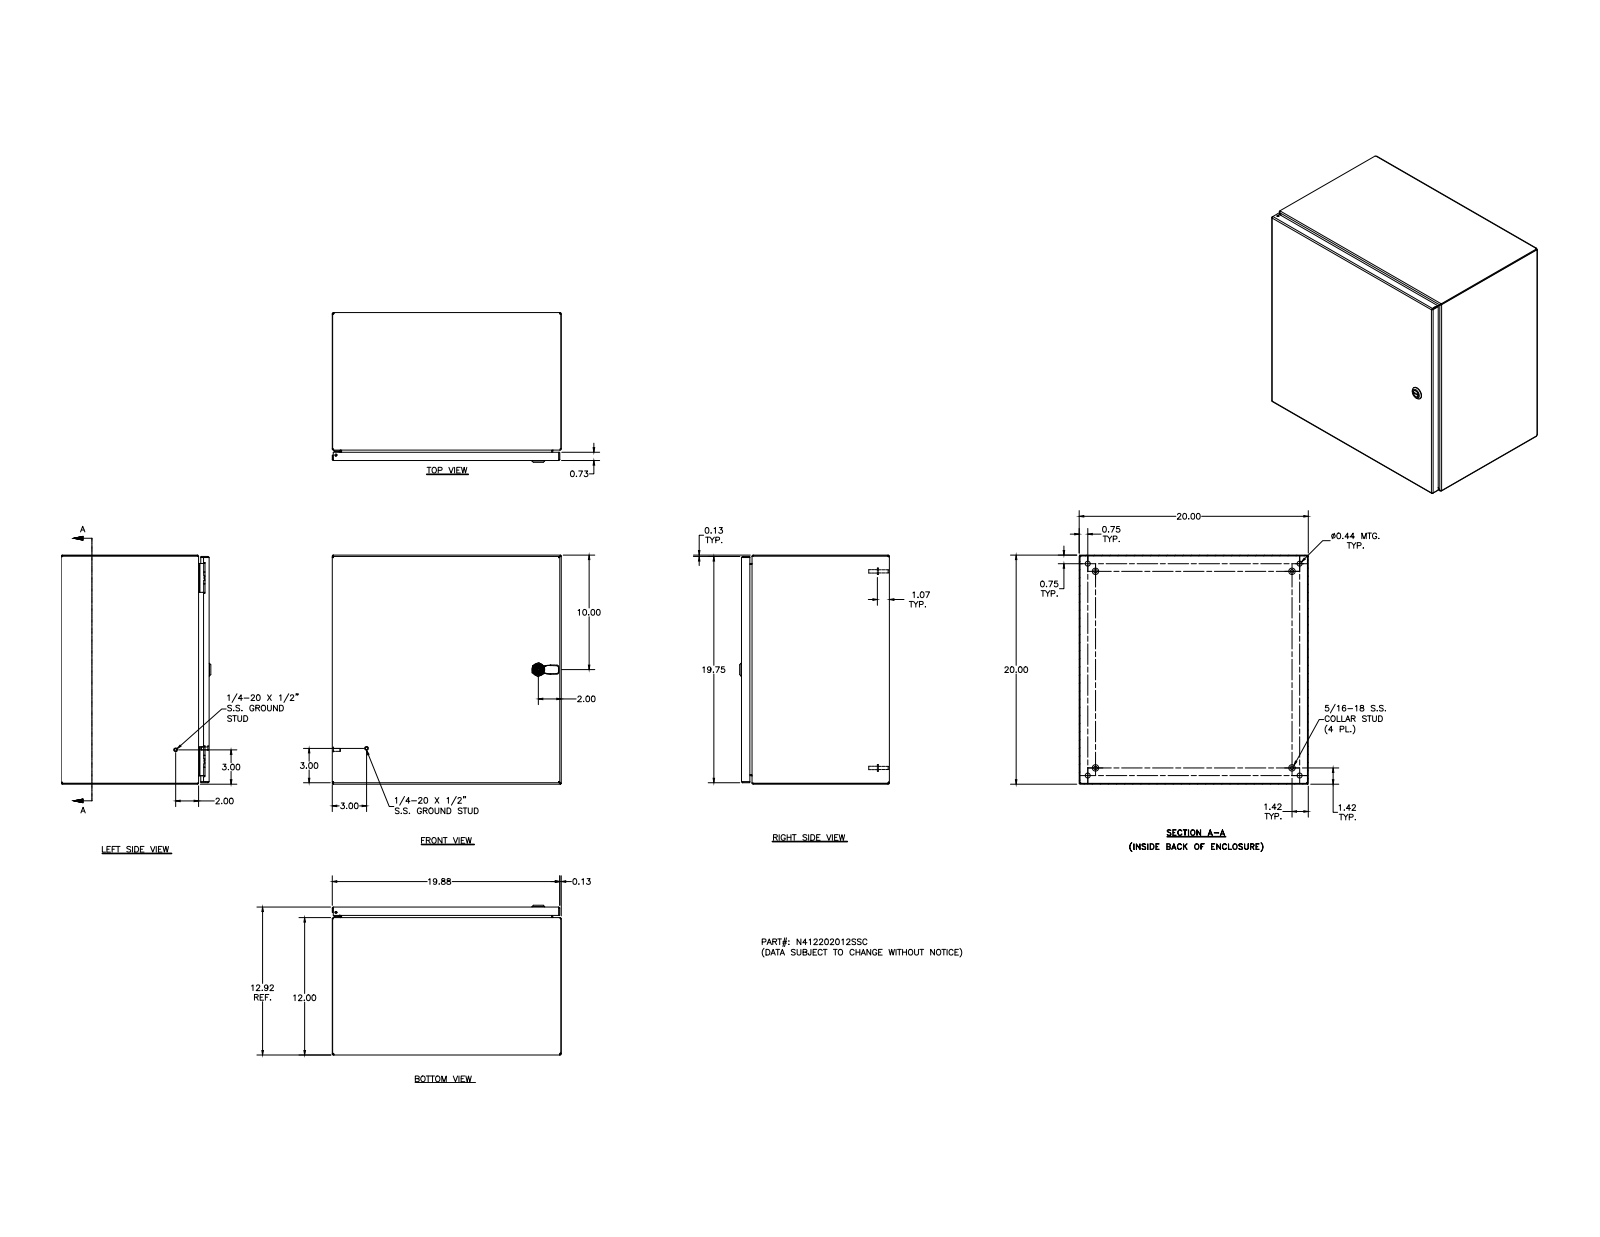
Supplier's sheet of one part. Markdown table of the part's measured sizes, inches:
| quantity | value |
| --- | --- |
| part name | N412202012SSC; N412202012SSCBKP; 388151; N4122020SSCLID (+8 more) |
| STEP written by | Autodesk Inventor 2011 (AUTOMOTIVE_DESIGN) |
| units | inches |
| bodies | 34 solids, 1384 faces (531 planar, 509 cylindrical, 344 other) |
| overall size | 20 × 20 × 13.075 |
| volume | 142.2 in³ |
| surface area | 3 864 in² |
| round holes (diameter × count) | 0.188 × 5, 0.093 × 4, 0.152 × 4, 0.167 × 4, 0.172 × 4, 0.437 × 4, 0.156 × 2, 0.187 × 1, 0.197 × 1, 0.315 × 1, 0.394 × 1, 0.402 × 1 |
| round bosses / shafts (diameter × count) | 0.25 × 10, 0.563 × 4, 0.36 × 4, 0.32 × 4, 0.3 × 4, 0.275 × 4, 0.256 × 4, 0.164 × 4 |
| partial cylindrical surfaces (radius × count) | 0.031 × 30, 0.05 × 26, 0.105 × 20, 0.016 × 18, 0.125 × 14, 0.02 × 9, 0.032 × 8, 0.07 × 8 |
| main face-to-face distances | 0.074, 19.926, 12.843, 19.852, 20, 12.769, 12.917, 11.926, 0.917, 0.739 |
| hole center spacings | 16, 0.017, 0.66, 16.008, 18.5, 18.872, 0.019, 0.5 |
